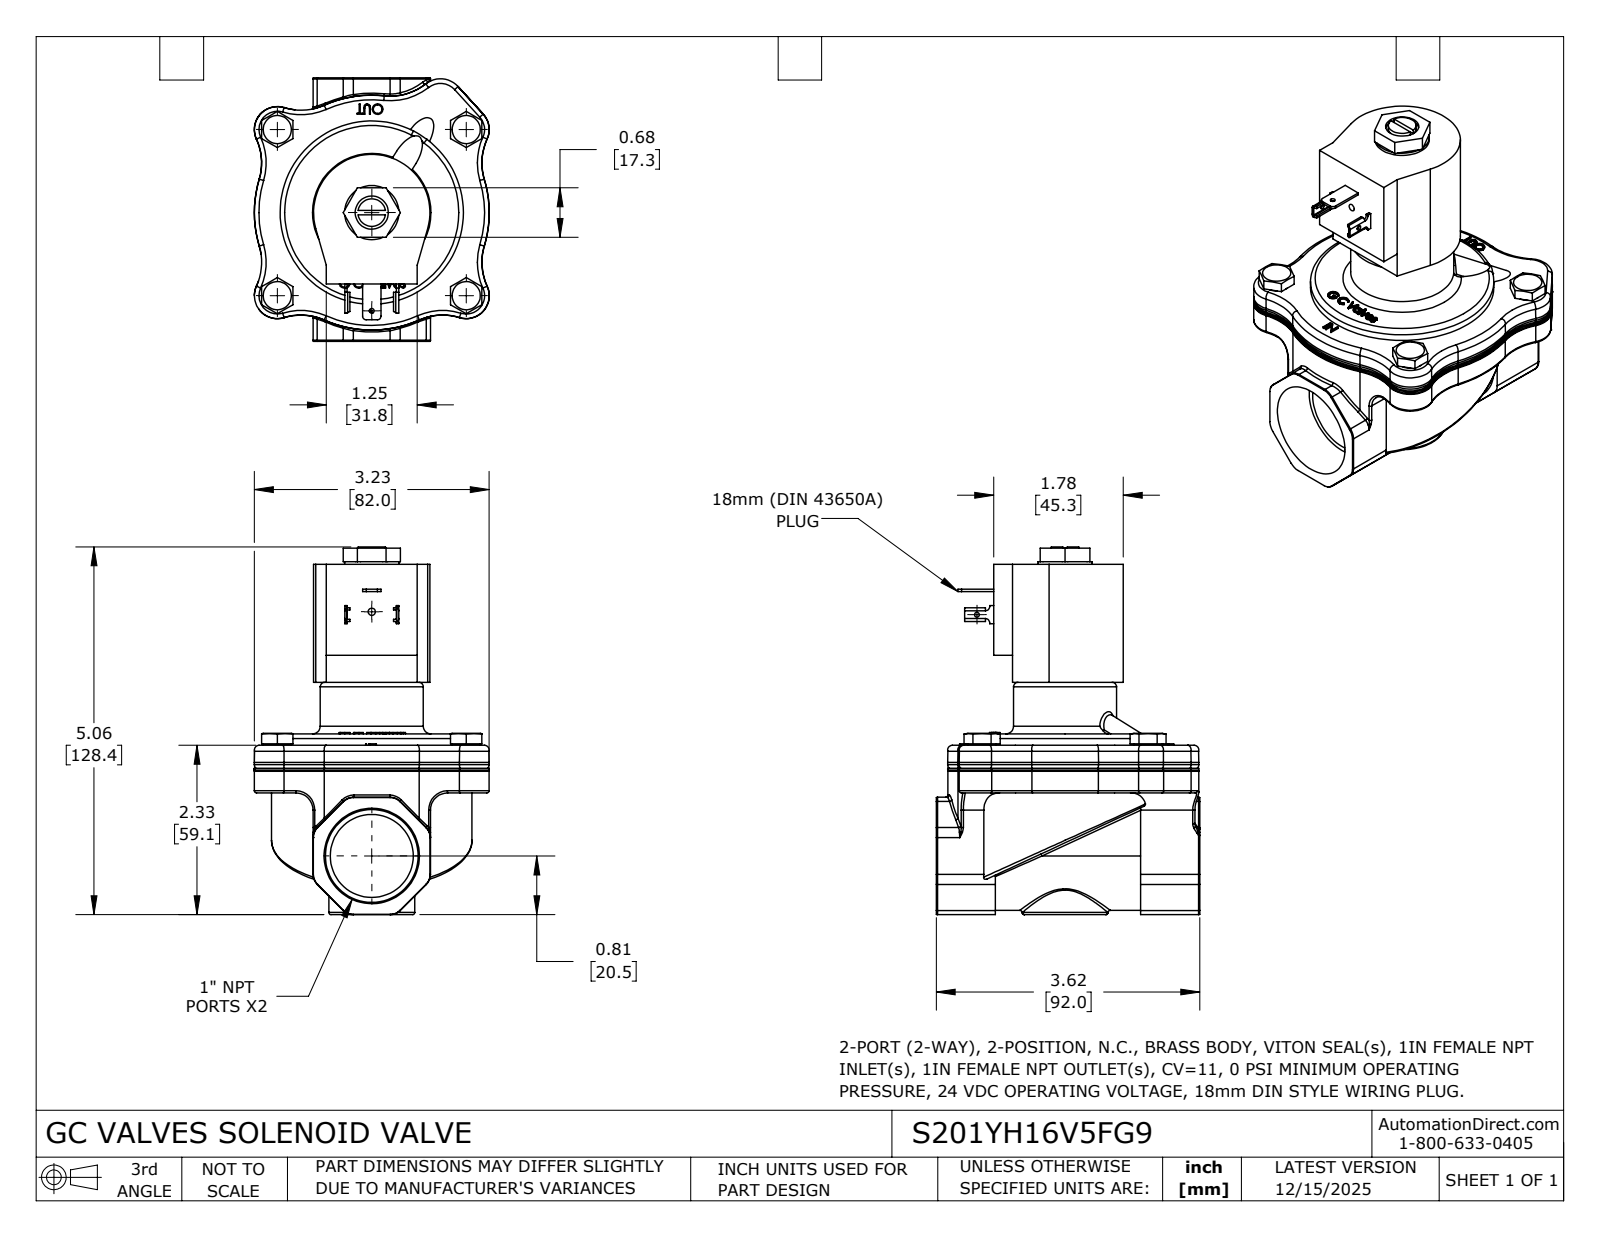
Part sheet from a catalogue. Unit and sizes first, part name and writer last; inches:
Units: inches
Overall size (bounding box): 5.055 × 3.622 × 3.232
Round holes (diameter × count): ⌀0.066 ×1, ⌀0.067 ×1, ⌀0.1 ×1, ⌀0.456 ×1, ⌀1.141 ×1
Round bosses / shafts (diameter × count): ⌀0.388 ×4, ⌀2.52 ×1, ⌀1.417 ×1, ⌀1.181 ×1, ⌀0.746 ×1, ⌀0.38 ×1
Partial cylindrical surfaces — rounded edges, fillets, slot ends (radius × count): R0.031 ×24, R0.787 ×24, R0.315 ×12, R0.197 ×8, R0.006 ×4, R0.041 ×4, R0.05 ×2, R0.06 ×2
Main face-to-face distances: 0.157, 0.655, 0.812, 3.141, 2.486, 2.329, 2.485, 2.328, 1.673, 4.814
Hole centre spacings: 1.35, 3.356
Volume: 19.13 in³ · Surface area: 70.49 in²
Bodies: 1 solid, 671 faces (220 planar, 172 cylindrical, 279 other)
Part name (STEP PRODUCT): S201YH16V5FG9
STEP written by: SolidWorks 2024 (CONFIG_CONTROL_DESIGN)
